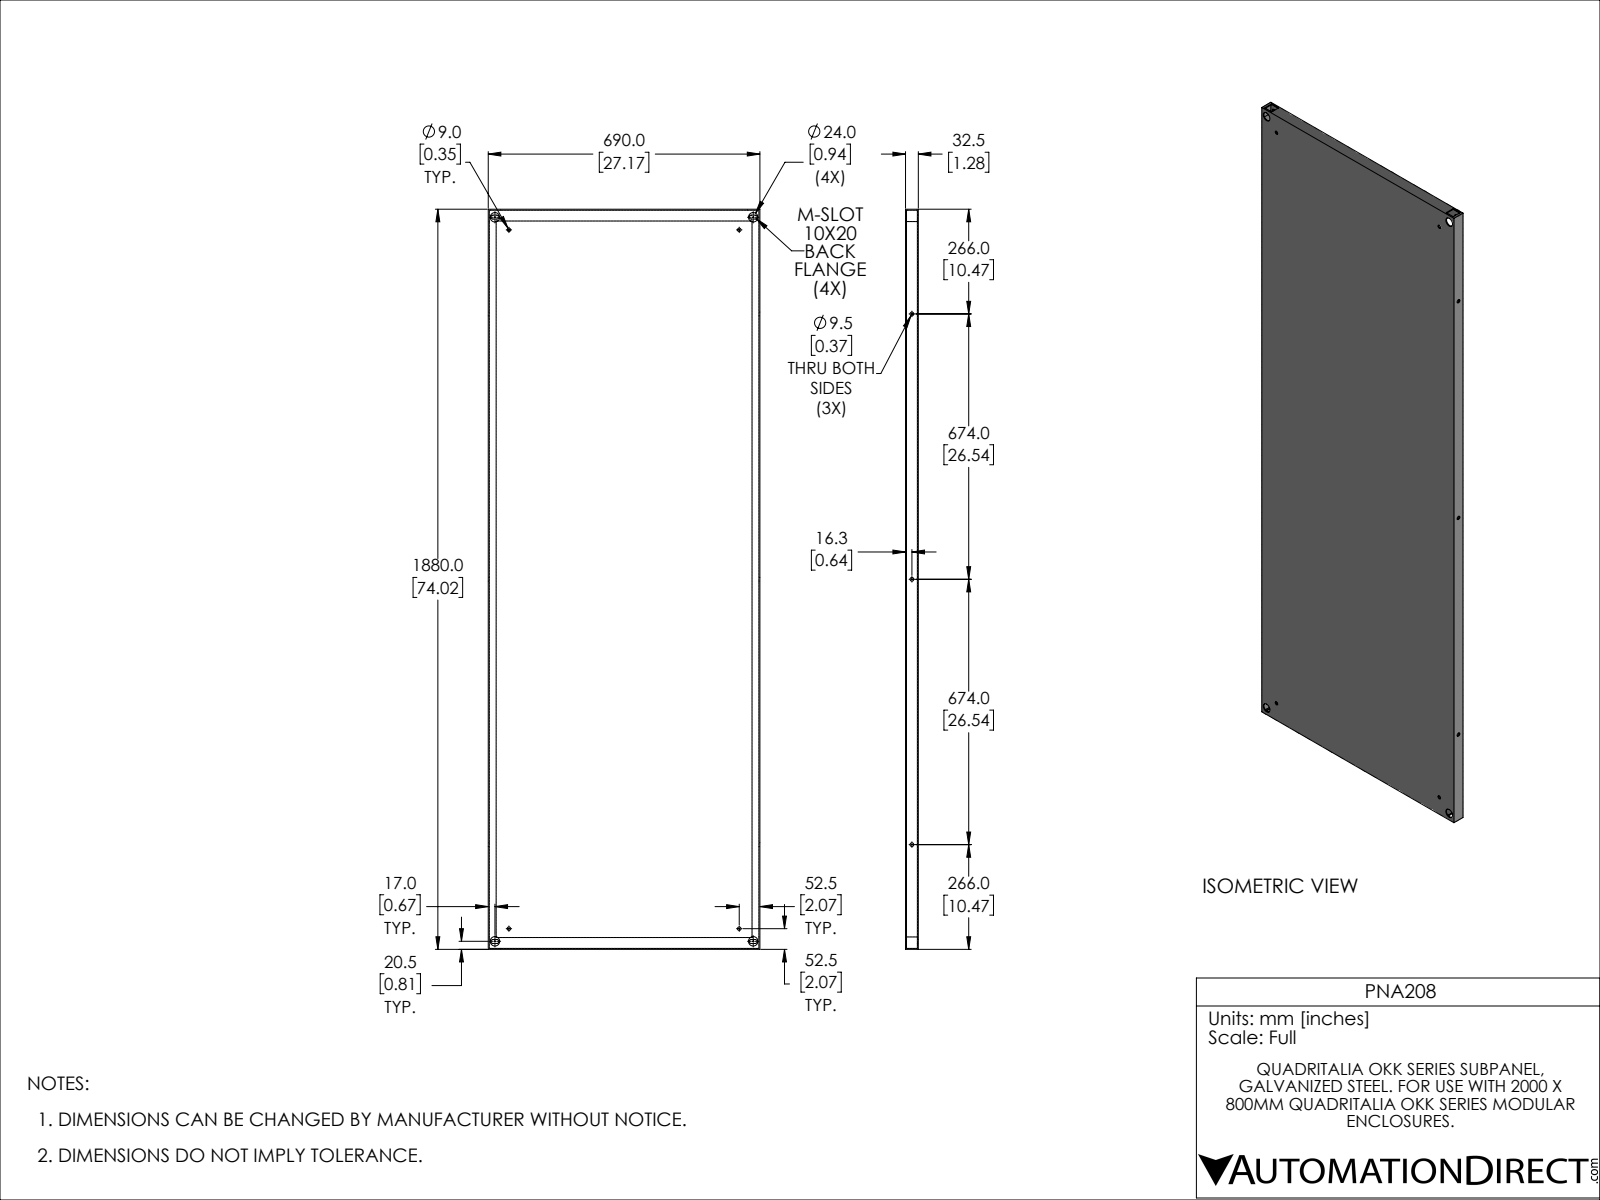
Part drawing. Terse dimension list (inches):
name: PNA208
written by: SolidWorks 2021 (CONFIG_CONTROL_DESIGN)
unit: in
bodies: 1 solid, 70 faces (48 planar, 22 cylindrical, 0 other)
size: 74.016 × 27.165 × 1.28
volume: 236 in³; area: 4 819 in²
holes: 4× ⌀0.354, 4× ⌀0.945, 3× ⌀0.374
rounds: 8× R0.197
face distances: 0.098, 1.181, 1.28, 1.083, 27.067, 27.165, 26.969, 73.917, 74.016, 73.819
hole spacings: 1.881, 24.461, 71.156, 75.219, 23.031, 25.827, 26.535, 69.882
